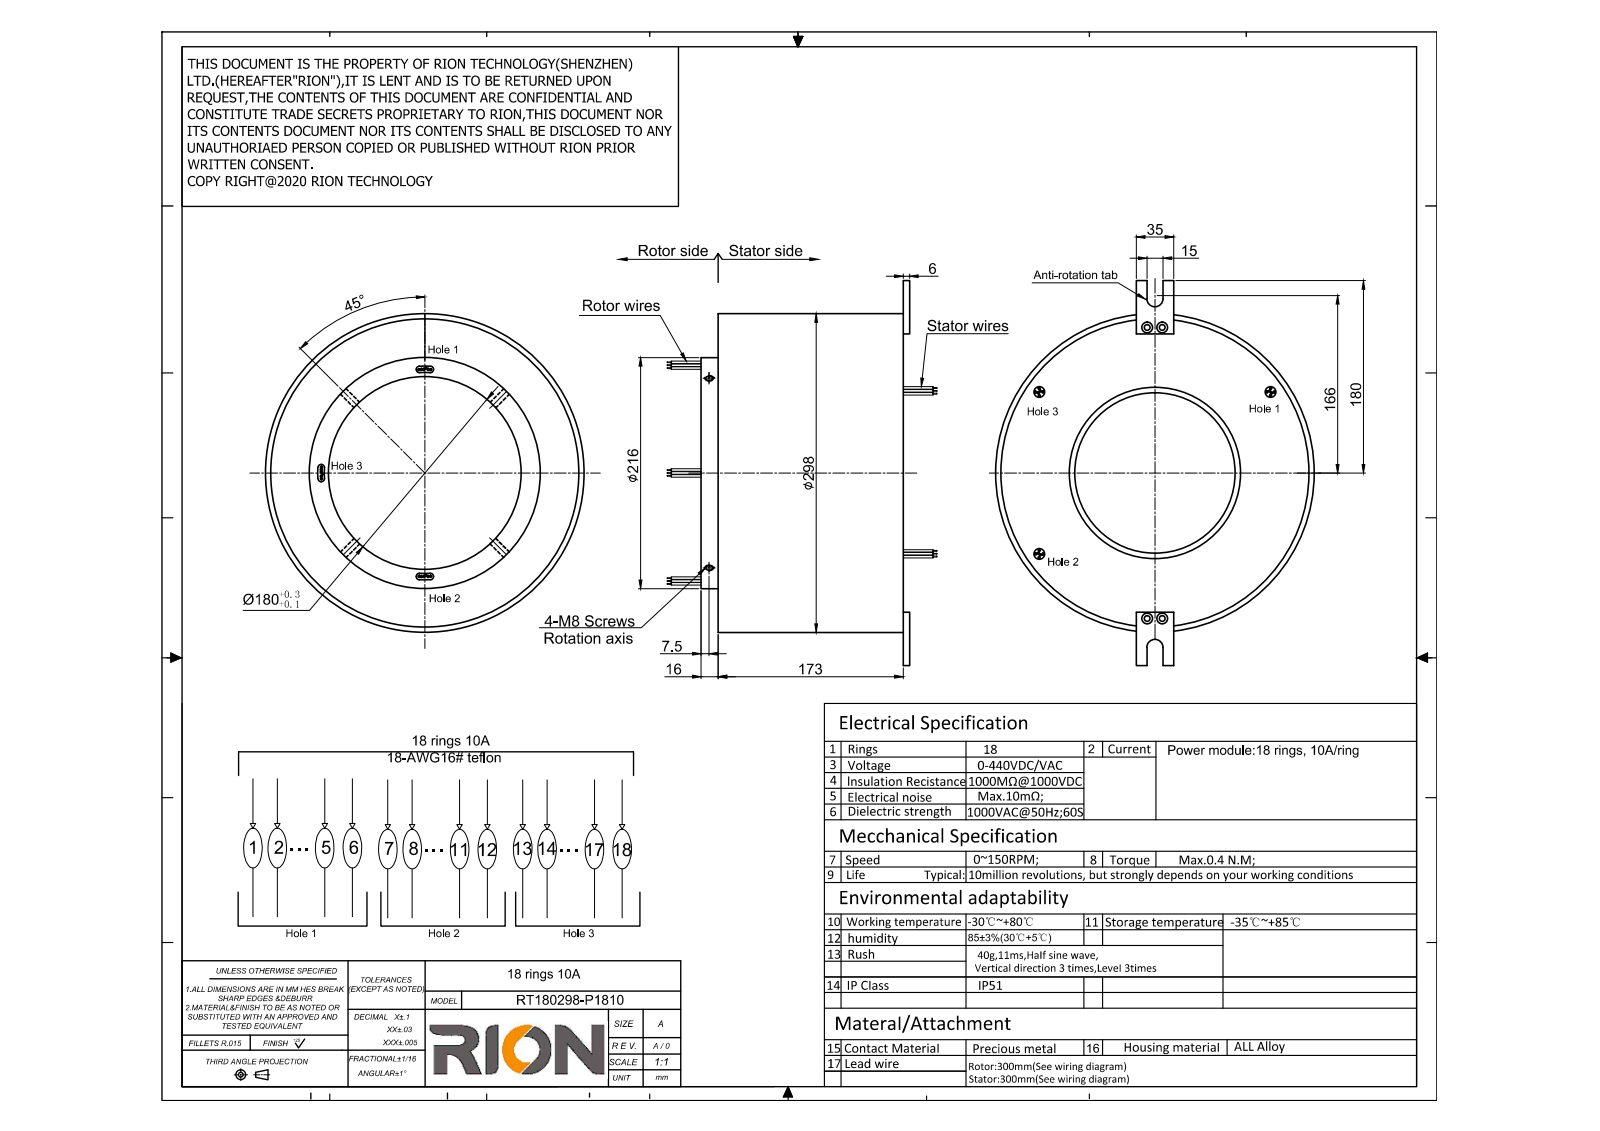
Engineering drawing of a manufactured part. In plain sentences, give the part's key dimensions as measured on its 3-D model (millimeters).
The part is named "RT180298-P1810". Its 3-D file was written by "SolidWorks 2014 (CONFIG_CONTROL_DESIGN)". It is 1 solid with 230 faces: 76 planar, 138 cylindrical and 16 other. Overall it measures 360 by 306 by 298 millimeters. Its volume is 7 860 000 cubic millimeters and its surface area 412 126 square millimeters. Round holes: 4 of diameter 4.2, 4 of diameter 5.2, 4 of diameter 6.8, 3 of diameter 10, 1 of diameter 180, 1 of diameter 190.2, 1 of diameter 290. Round bosses or shafts: 18 of diameter 2.1, 18 of diameter 1.3, 1 of diameter 298, 1 of diameter 289.8, 1 of diameter 216, 1 of diameter 190. Partial cylindrical surfaces (rounded edges, fillets, slot ends): 6 of radius 3, 2 of radius 7.5, 1 of radius 94.45, 1 of radius 100.45. The main face-to-face distances are 173, 16, 189, 195, 179, 6, 3, 35, 15, 10. The hole center spacings are 132, 14.34, 116.31, 128.78, 136.12, 136.28, 235.2, 241.79.
